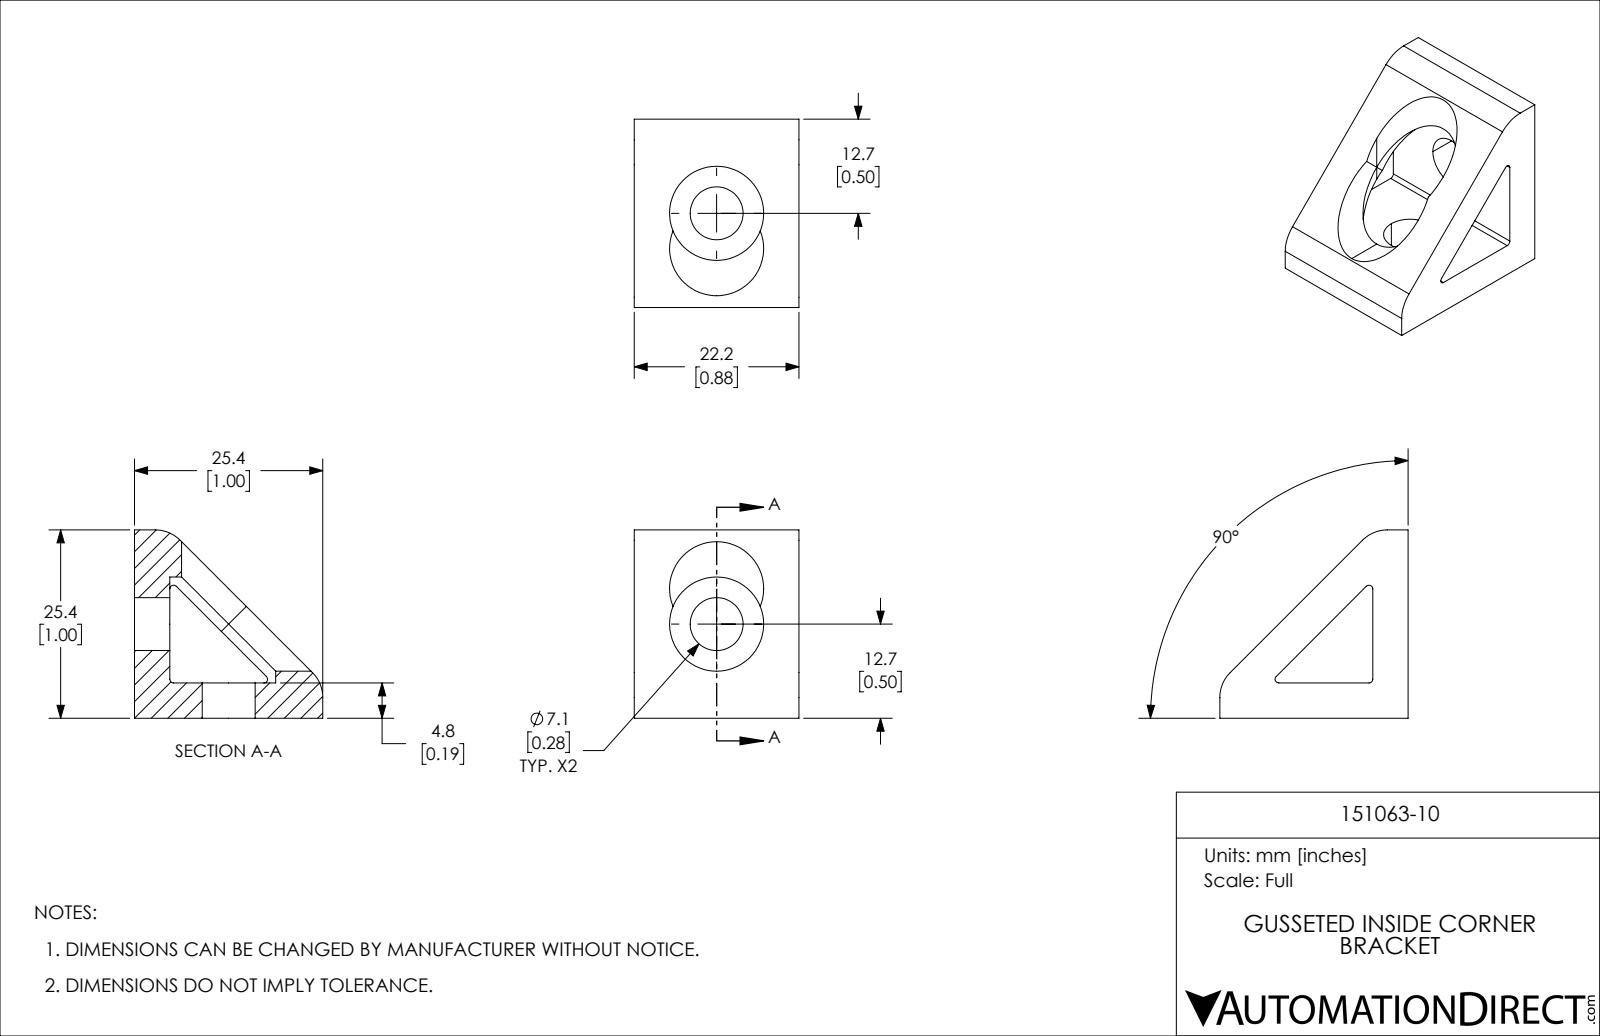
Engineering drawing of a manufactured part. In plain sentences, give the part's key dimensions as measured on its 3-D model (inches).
The part is named "151063-10". Its 3-D file was written by "SolidWorks 2024 (CONFIG_CONTROL_DESIGN)". It is 1 solid with 31 faces: 11 planar, 20 cylindrical and 0 other. Overall it measures 1 by 1 by 0.875 inches. Its volume is 0.369 cubic inches and its surface area 5.481 square inches. Round holes: 2 of diameter 0.281, 2 of diameter 0.5. Partial cylindrical surfaces (rounded edges, fillets, slot ends): 3 of radius 0.02, 1 of radius 0.187, 1 of radius 0.188. The main face-to-face distances are 0.187, 0.875, 1, 0.813.
